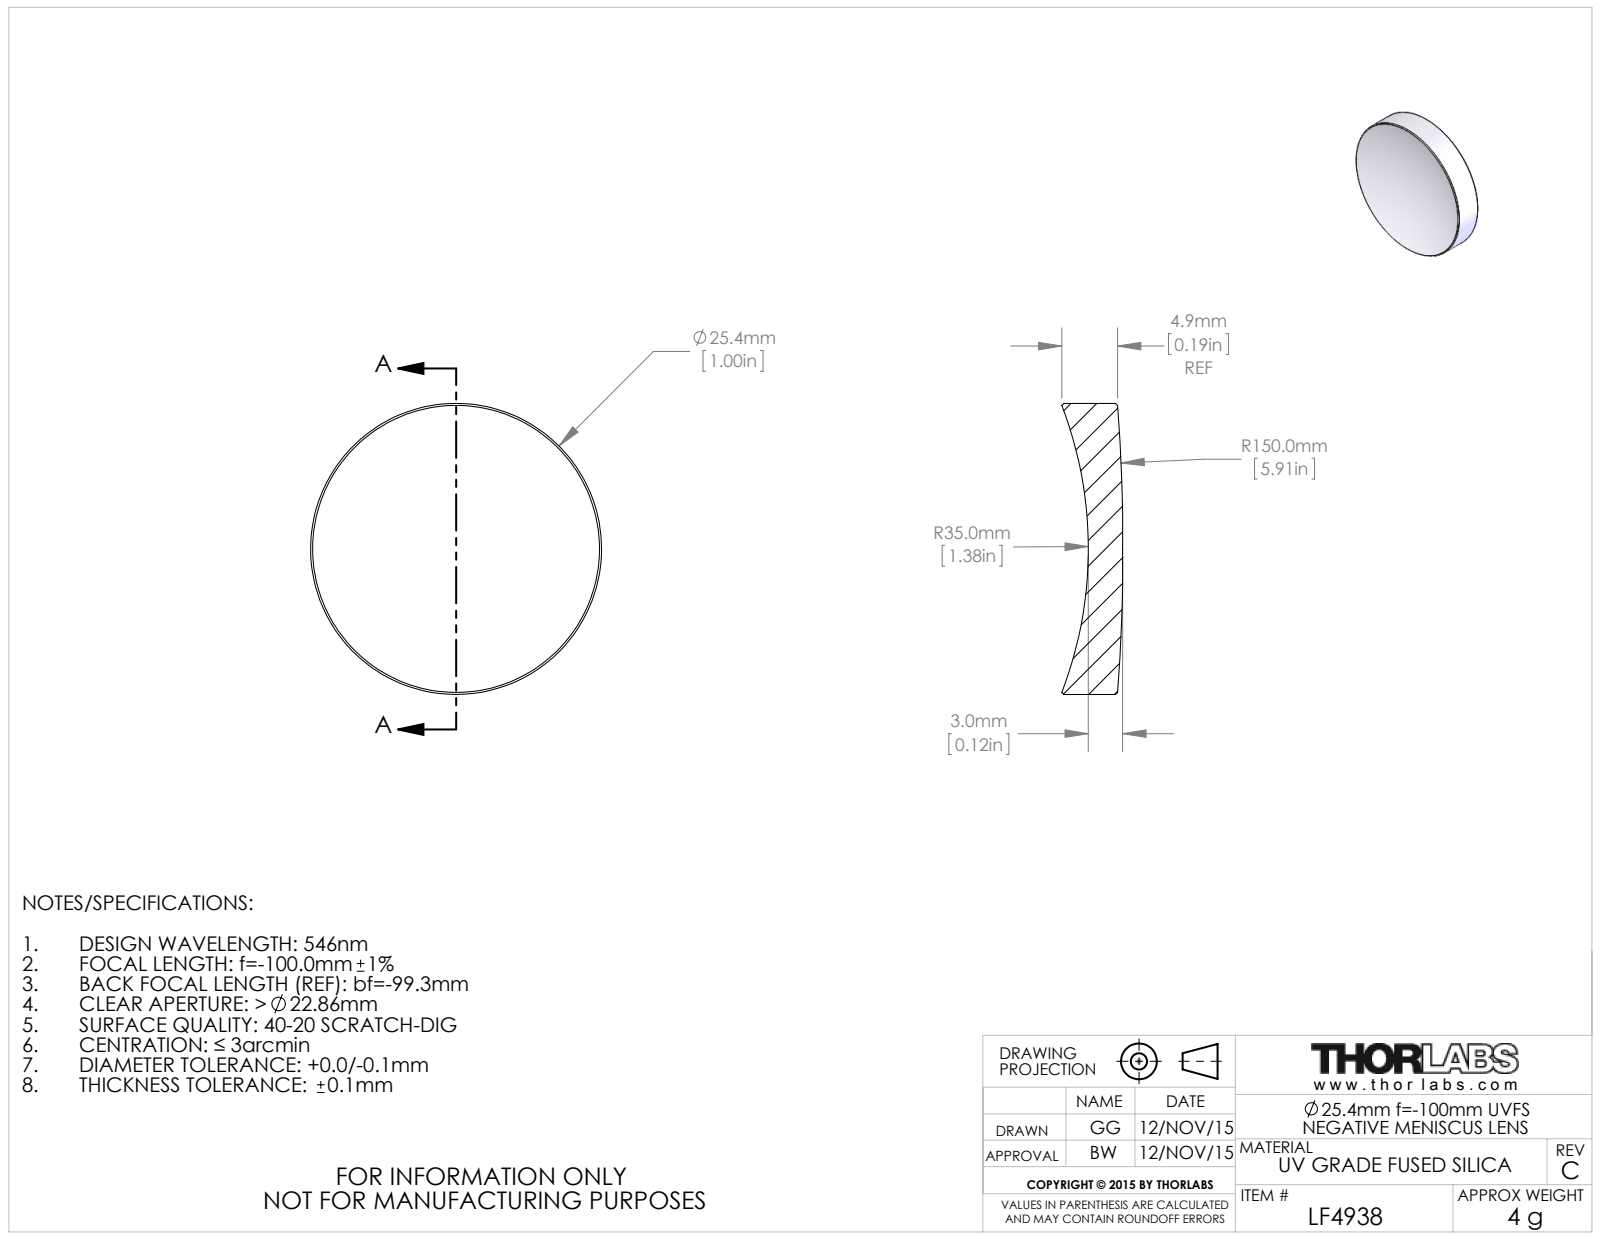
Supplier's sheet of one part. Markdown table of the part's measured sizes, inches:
| quantity | value |
| --- | --- |
| part name | 4218-E0W |
| STEP written by | SolidWorks 2014 (CONFIG_CONTROL_DESIGN) |
| units | inches |
| bodies | 1 solid, 10 faces (0 planar, 2 cylindrical, 8 other) |
| overall size | 1 × 1 × 0.209 |
| volume | 0.122 in³ |
| surface area | 2.173 in² |
| round bosses / shafts (diameter × count) | 1 × 1 |
